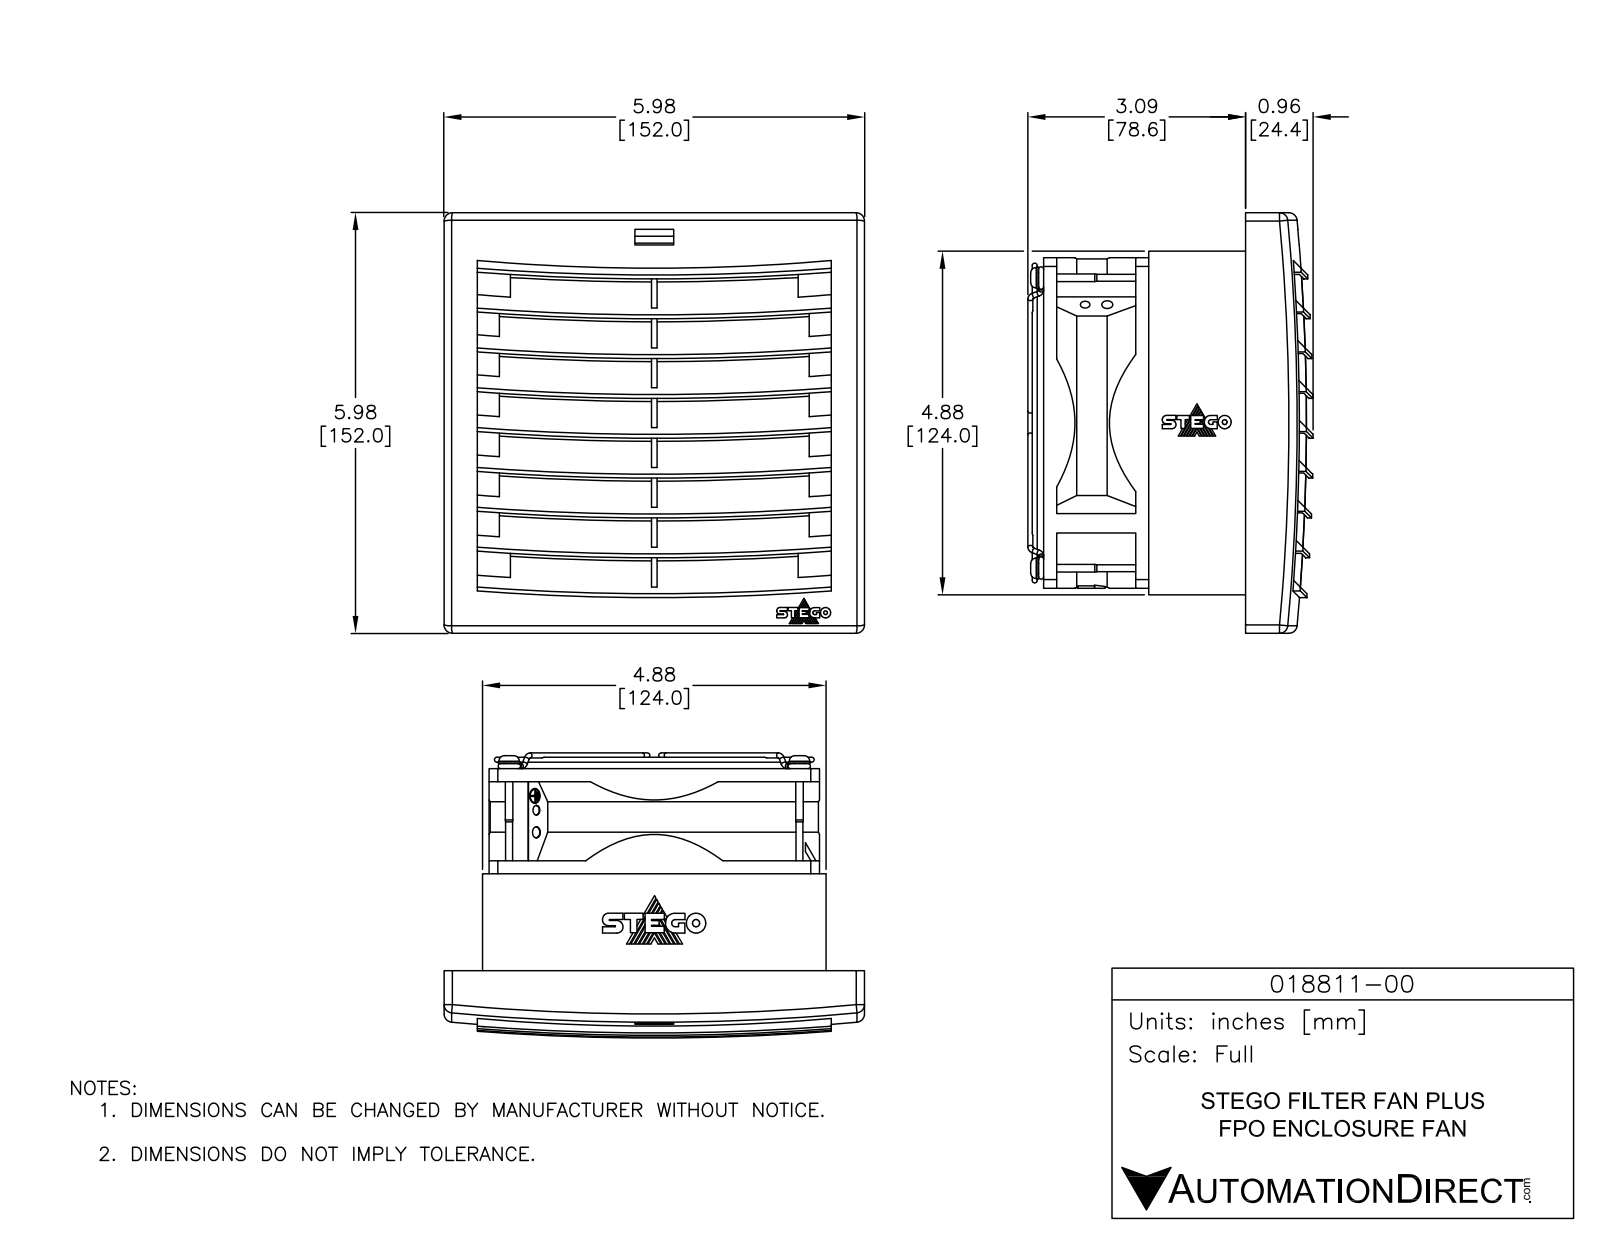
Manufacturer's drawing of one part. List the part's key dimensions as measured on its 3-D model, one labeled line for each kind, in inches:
Part name (STEP PRODUCT): PRODUCT_NAME_1
STEP written by: ACIS (AUTOMOTIVE_DESIGN_CC2)
Units: inches
Bodies: 1 solid, 579 faces (331 planar, 236 cylindrical, 12 other)
Overall size (bounding box): 5.985 × 5.984 × 4.094
Volume: 32.77 in³ · Surface area: 359.5 in²
Round holes (diameter × count): ⌀0.256 ×4, ⌀0.98 ×1, ⌀1.66 ×1, ⌀2.34 ×1, ⌀3.02 ×1, ⌀3.254 ×1, ⌀3.78 ×1, ⌀4.15 ×1
Round bosses / shafts (diameter × count): ⌀4.346 ×1, ⌀3.49 ×1, ⌀3.178 ×1, ⌀2.712 ×1, ⌀2.498 ×1, ⌀1.817 ×1, ⌀1.323 ×1, ⌀1.137 ×1
Partial cylindrical surfaces — rounded edges, fillets, slot ends (radius × count): R13.757 ×16, R1.852 ×5, R0.118 ×4, R0.142 ×4, R0.519 ×1, R0.849 ×1, R0.967 ×1, R1.238 ×1
Main face-to-face distances: 0.059, 0.426, 0.122, 4.76, 0.852, 0.079, 0.135, 0.269, 0.485, 0.367
Hole centre spacings: 3.007, 4.252, 6.013
